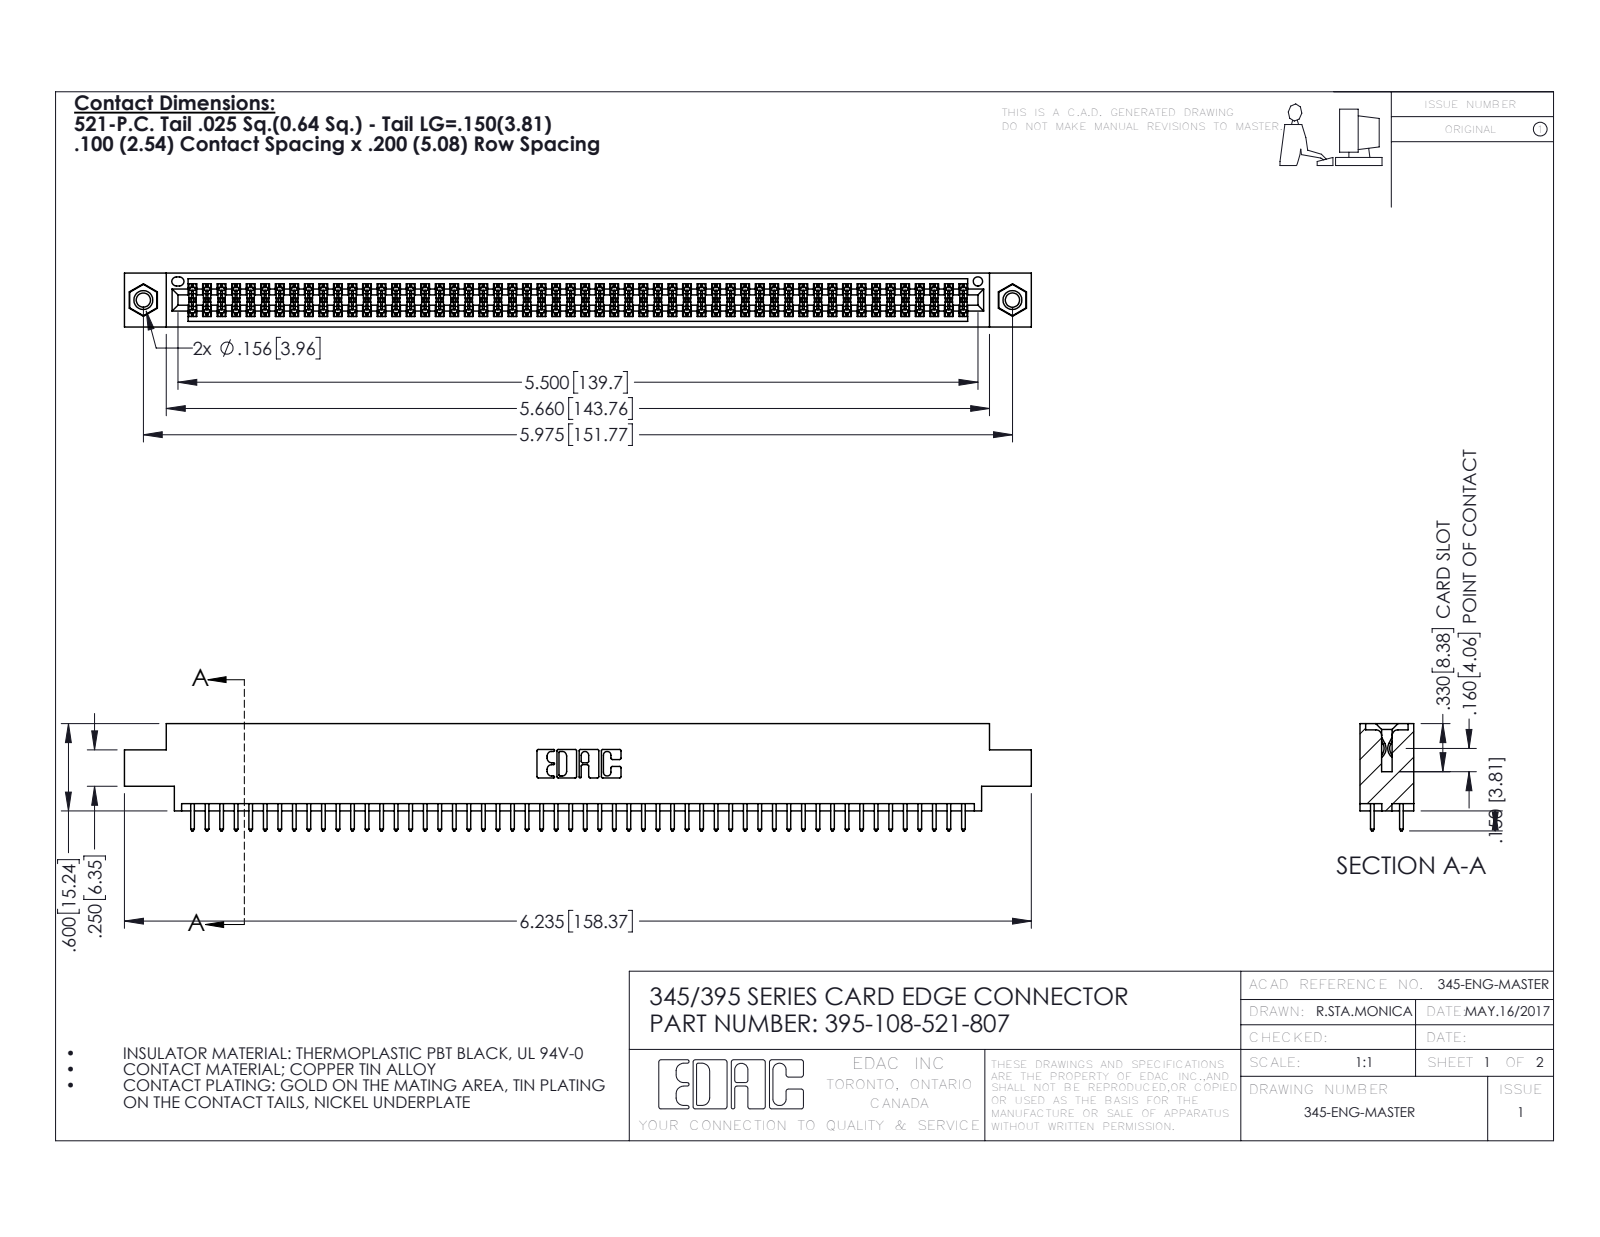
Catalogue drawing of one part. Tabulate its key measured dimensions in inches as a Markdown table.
| quantity | value |
| --- | --- |
| part name | 345 Part_0.170 Offset - 0.156 Dia-TI; 345-250-001_345-250-005-103; 395-108-521-807; 345-292-001_345-293-121 |
| STEP written by | SolidWorks 2016 (CONFIG_CONTROL_DESIGN) |
| units | inches |
| bodies | 111 solids, 5590 faces (3680 planar, 1894 cylindrical, 16 other) |
| overall size | 6.235 × 0.737 × 0.37 |
| volume | 0.935 in³ |
| surface area | 35.29 in² |
| round holes (diameter × count) | 0.098 × 2, 0.125 × 2, 0.156 × 2, 0.064 × 1 |
| round bosses / shafts (diameter × count) | 0.155 × 2 |
| partial cylindrical surfaces (radius × count) | 0.006 × 162, 0.01 × 108, 0.01 × 22, 0.007 × 6, 0.031 × 6, 0.026 × 3, 0.014 × 2, 0.019 × 2 |
| main face-to-face distances | 0.072, 0.298, 0.2, 0.37, 0.098, 0.272, 0.025, 0.225, 0.175, 0.149 |
| hole center spacings | 0.27, 5.739, 5.975 |
